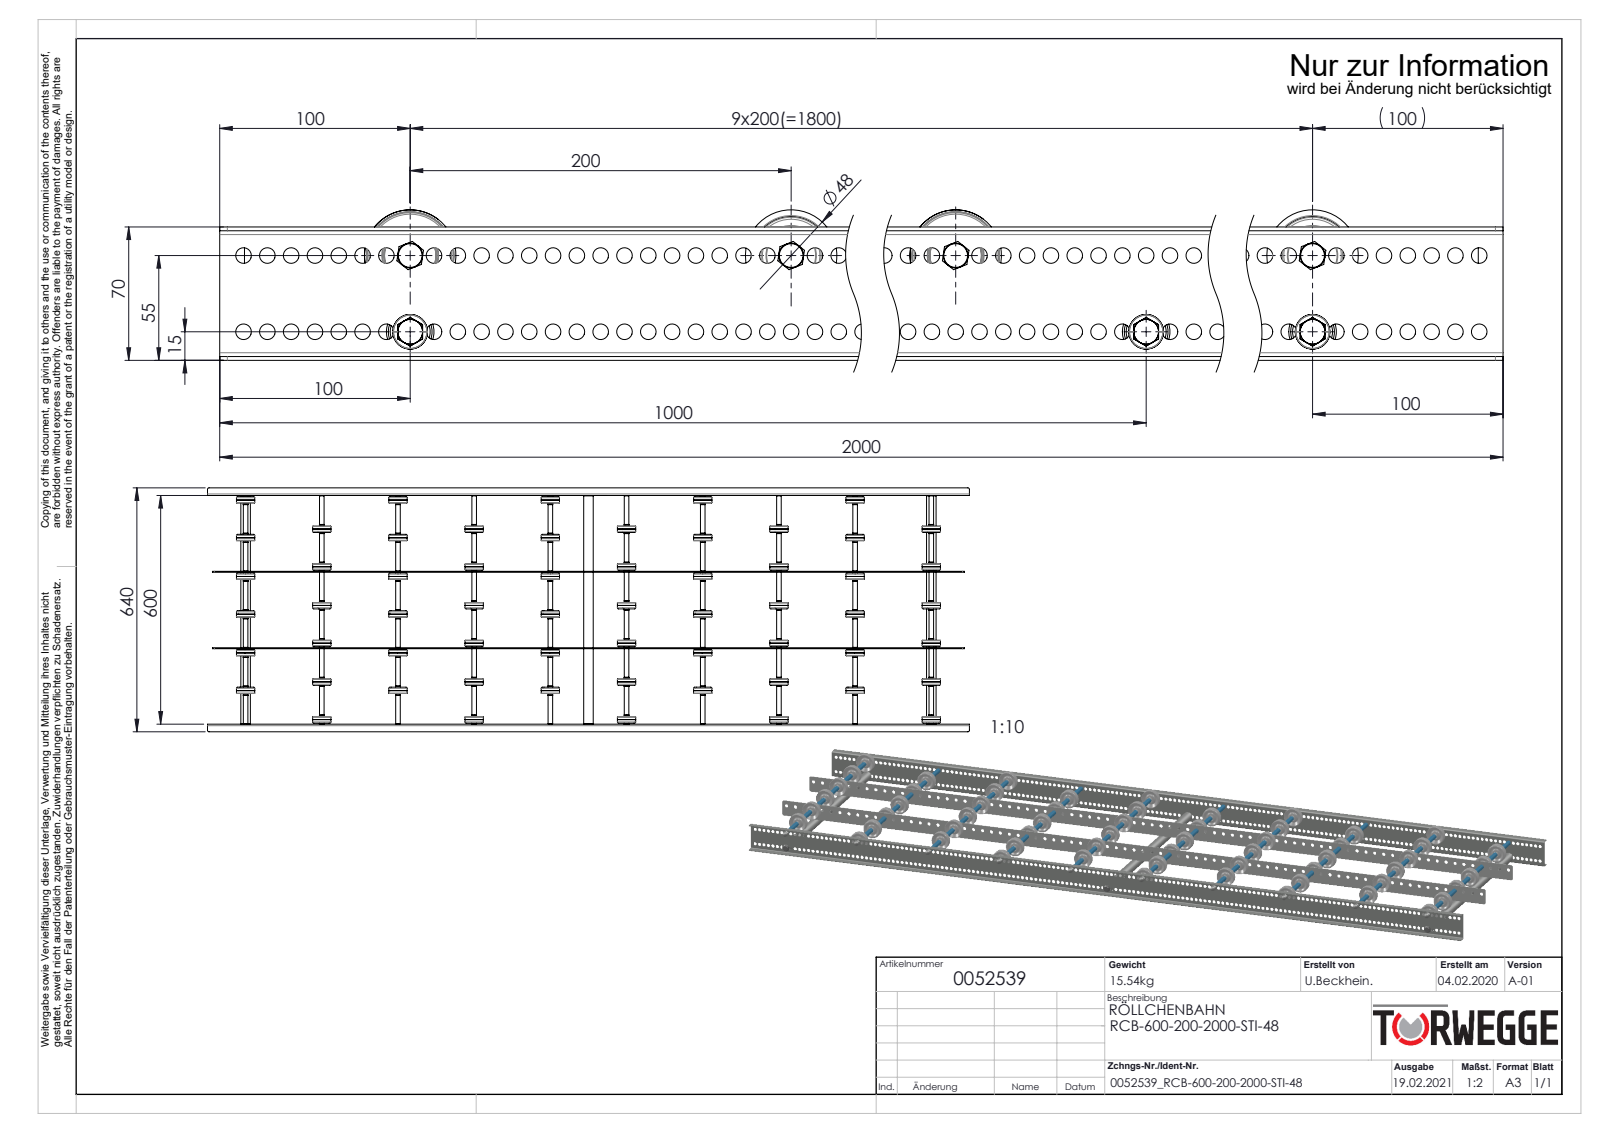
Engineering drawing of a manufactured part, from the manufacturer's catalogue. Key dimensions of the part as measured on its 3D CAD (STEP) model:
Part name (STEP PRODUCT): S100994_Sperrzahnschraube_M08x16-8.8-A2K; Röllchenachse-für-Konfiguration_EL600 Stahl; S100100_Längstraverse-42x2,5_S100103_Lngstraverse-RB-L2000; Profil_LRB-20x70x20x2_KFG_S100202_U-PROFIL-20-70-20-2-LRB-L=2000 (+6 more)
STEP written by: SolidWorks 2020 (AUTOMOTIVE_DESIGN)
Units: millimetres
Bodies: 229 solids, 7802 faces (1434 planar, 3572 cylindrical, 2796 other)
Overall size (bounding box): 2000 × 640 × 79
Volume: 3 222 000 mm³ · Surface area: 2 653 000 mm²
Round holes (diameter × count): ⌀8.2 ×318, ⌀8.5 ×79, ⌀6.65 ×10, ⌀8 ×10, ⌀9.65 ×10, ⌀15 ×10, ⌀41 ×10, ⌀6.8 ×3, ⌀21 ×3
Round bosses / shafts (diameter × count): ⌀48 ×10, ⌀13 ×10, ⌀12.5 ×10, ⌀12.4 ×10, ⌀12 ×10, ⌀11.5 ×10, ⌀25 ×3, ⌀8 ×3
Partial cylindrical surfaces — rounded edges, fillets, slot ends (radius × count): R4 ×8, R2 ×4, R5 ×4
Main face-to-face distances: 200.5, 2, 602, 2.5, 198, 401, 68, 604, 600, 76
Hole centre spacings: 12.5, 25, 37.5, 50, 62.5, 75, 87.5, 100
